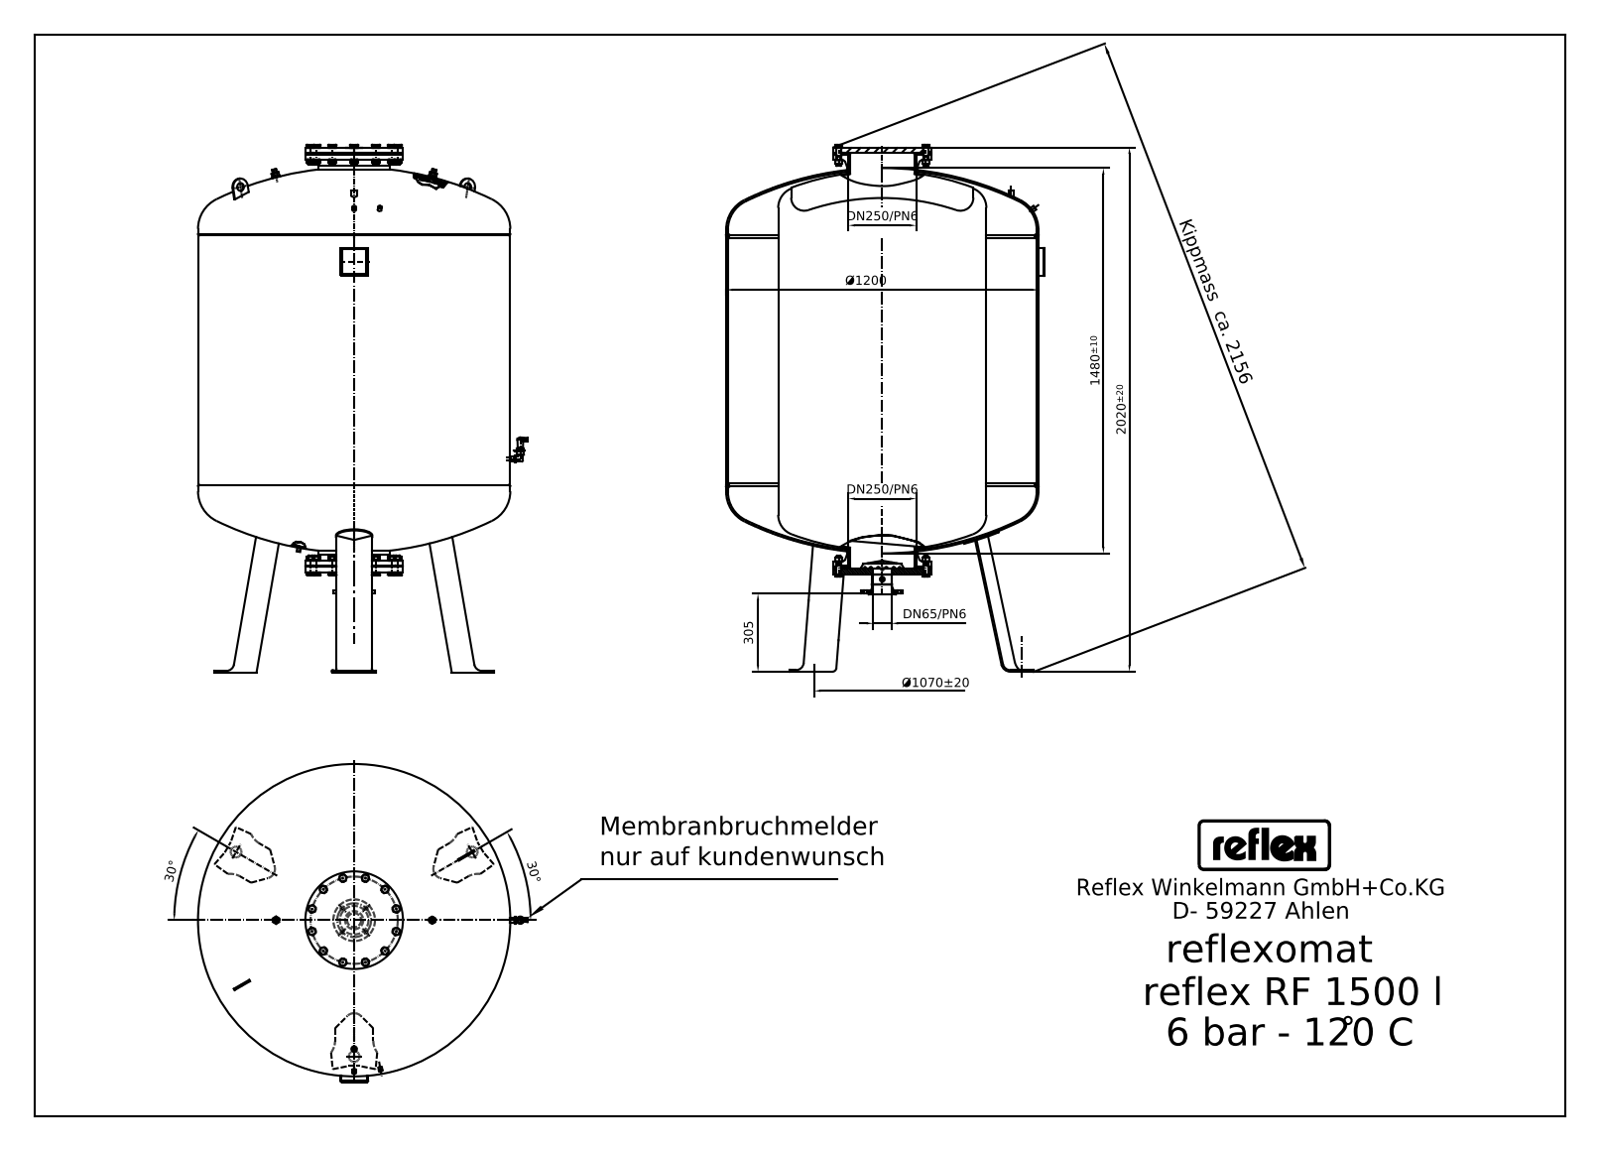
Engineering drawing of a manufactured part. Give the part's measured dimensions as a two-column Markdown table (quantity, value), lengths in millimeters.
| quantity | value |
| --- | --- |
| STEP written by | Mechanical Desktop 2009 (CONFIG_CONTROL_DESIGN) |
| units | millimeters |
| bodies | 23 solids, 940 faces (556 planar, 222 cylindrical, 162 other) |
| overall size | 2030 × 1266 × 1220 |
| volume | 1 502 000 000 mm³ |
| surface area | 13 230 000 mm² |
| round holes (diameter × count) | 11.45 × 2, 3.5 × 1, 14.95 × 1, 30 × 1, 260.4 × 1 |
| round bosses / shafts (diameter × count) | 16 × 12, 21.3 × 3, 18.5 × 3, 28 × 2, 20 × 2, 1200 × 1, 375 × 1, 273 × 1 |
| partial cylindrical surfaces (radius × count) | 25 × 18, 1 × 5, 8.44 × 4, 3.38 × 3, 6 × 3, 9 × 3, 2 × 2, 3 × 2 |
| main face-to-face distances | 970, 22, 1615, 27, 1588, 1283, 313, 1305, 335, 332 |
| hole center spacings | 495, 619.5, 792.97 |
